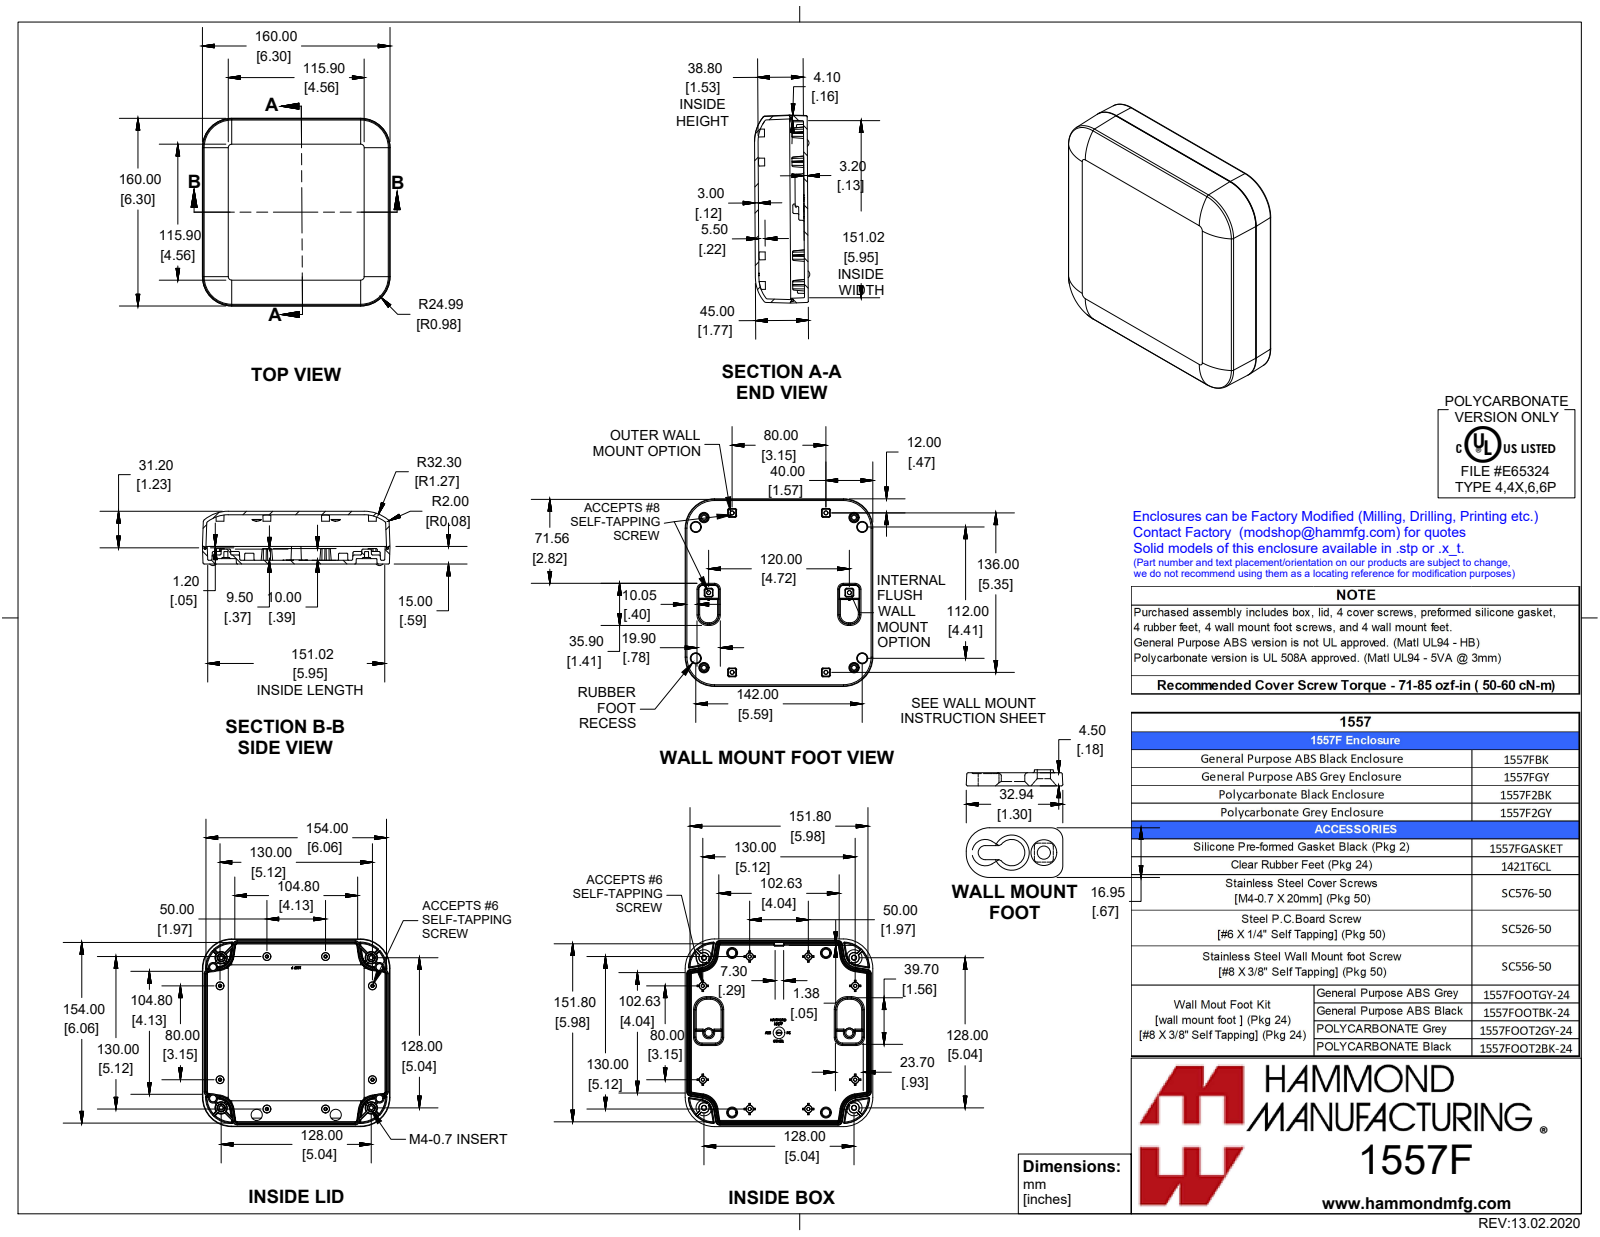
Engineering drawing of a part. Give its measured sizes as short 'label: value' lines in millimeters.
name: Wall Mount Foot; 1557F2GY; 1557F TOP; 1557F gasket (+5 more)
written by: SolidWorks 2019 (CONFIG_CONTROL_DESIGN)
unit: mm
bodies: 23 solids, 2849 faces (963 planar, 581 cylindrical, 1305 other)
size: 189 × 160 × 49.5
volume: 261 000 mm³; area: 184 300 mm²
holes: 4× ⌀3.3, 4× ⌀4.5
bosses: 12× ⌀1.8, 4× ⌀8, 4× ⌀7.7, 4× ⌀6.4, 4× ⌀5.5, 4× ⌀5.3, 4× ⌀4.2, 4× ⌀3.9
rounds: 101× R0.5, 78× R1, 12× R4, 8× R0.2, 8× R0.3, 8× R0.4, 8× R1.5, 8× R2.1
face distances: 3, 3.2, 42, 38.8, 45, 41.8, 156.8, 159.8, 4.1, 152.8
hole spacings: 24.3, 104.1, 128, 134.2, 168, 80, 136, 157.8
